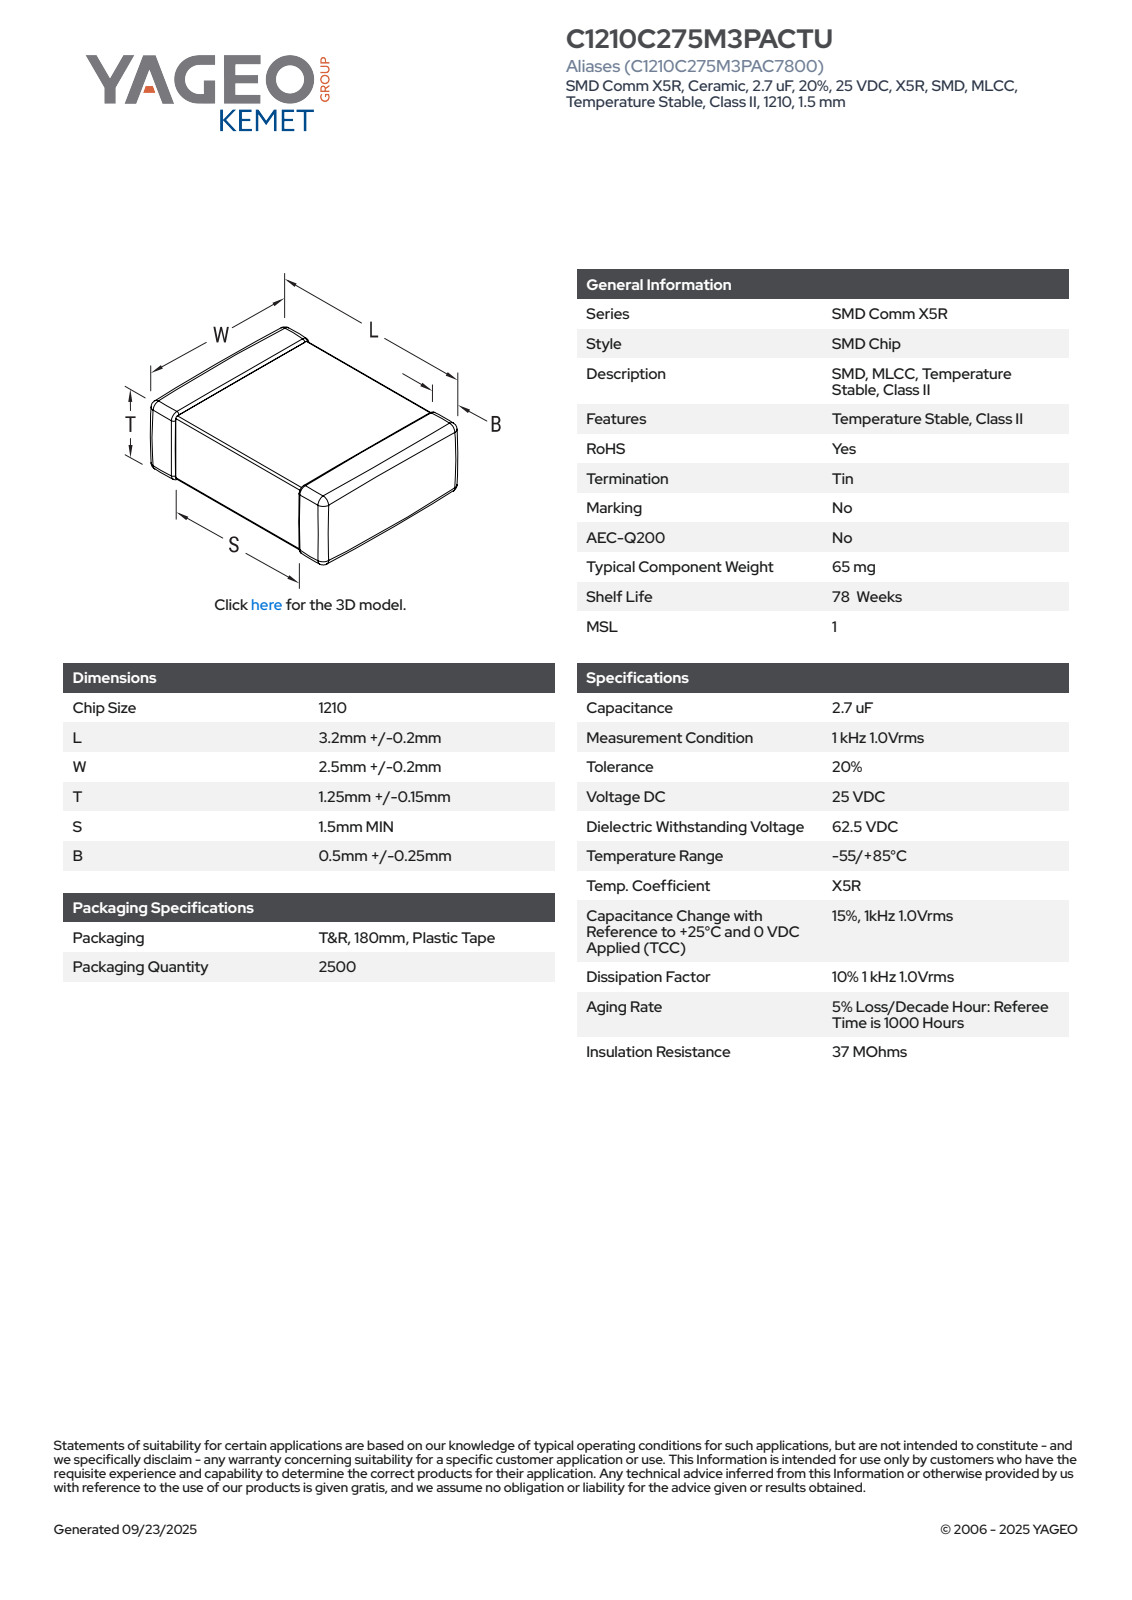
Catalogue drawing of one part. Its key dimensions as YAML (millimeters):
part_name: "CCS_CCSTD_1210_L3.4W2.7T1.4B0.5"
step_written_by: "SolidWorks 2021 (AUTOMOTIVE_DESIGN)"
units: millimeters
bodies: {solids: 4, faces: 125, planar: 71, cylindrical: 38, other: 16}
overall_size: [3.4, 2.7, 1.4]
volume: 12
surface_area: 35
face_to_face_distances: [1.34, 1.28, 3.4, 1.4, 2.64, 2.58, 2.7, 1.35, 1.29, 0.4]
